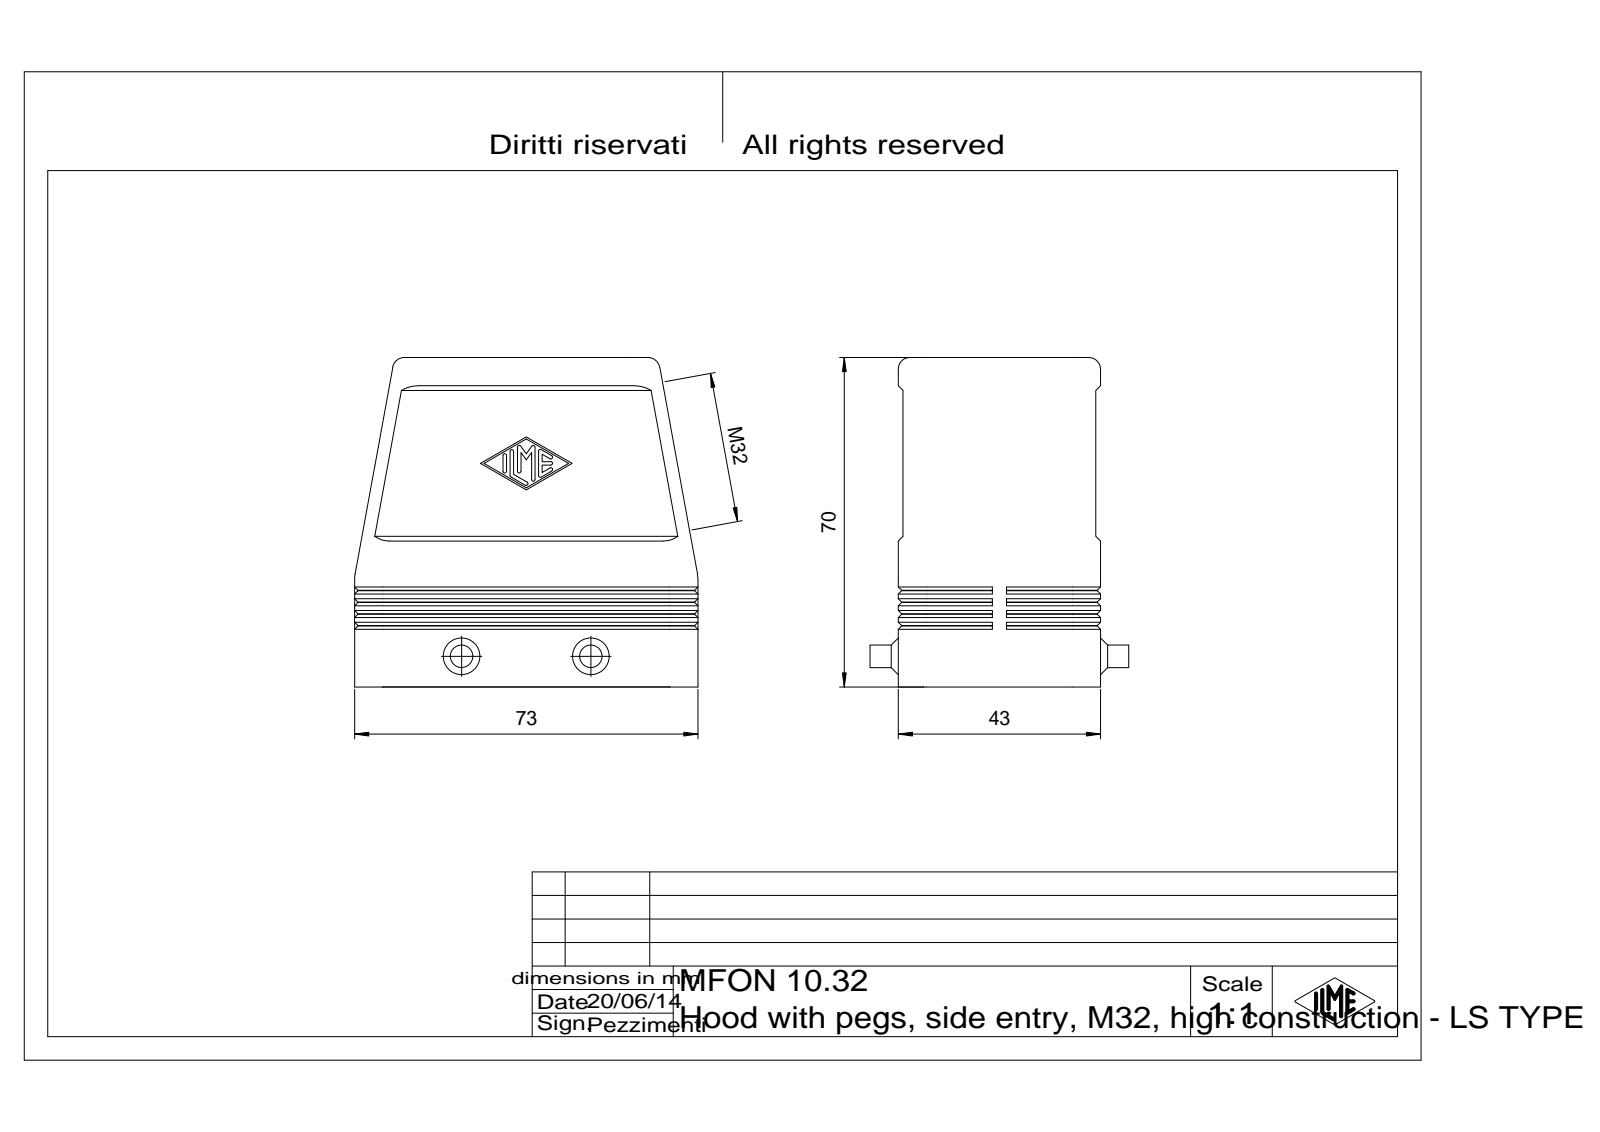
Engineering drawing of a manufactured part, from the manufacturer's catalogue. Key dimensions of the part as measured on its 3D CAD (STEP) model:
Part name (STEP PRODUCT): MFON_10.32
STEP written by: CoCreate Modeling 16.00A 16-Aug-2008 (C) Parametric Technology GmbH (AUTOMOTIVE_DESIGN)
Units: millimetres
Bodies: 0 solids, 331 faces (153 planar, 122 cylindrical, 56 other)
Overall size (bounding box): 73 × 70.01 × 55
Round holes (diameter × count): ⌀2.46 ×4, ⌀4 ×4, ⌀32 ×1
Round bosses / shafts (diameter × count): ⌀4.8 ×2
Partial cylindrical surfaces — rounded edges, fillets, slot ends (radius × count): R6 ×10, R2 ×4, R2.5 ×4, R3 ×4, R5.3 ×4
Main face-to-face distances: 4, 38, 3, 35, 1, 39, 42, 41, 11, 7
Hole centre spacings: 27, 57, 63.07
